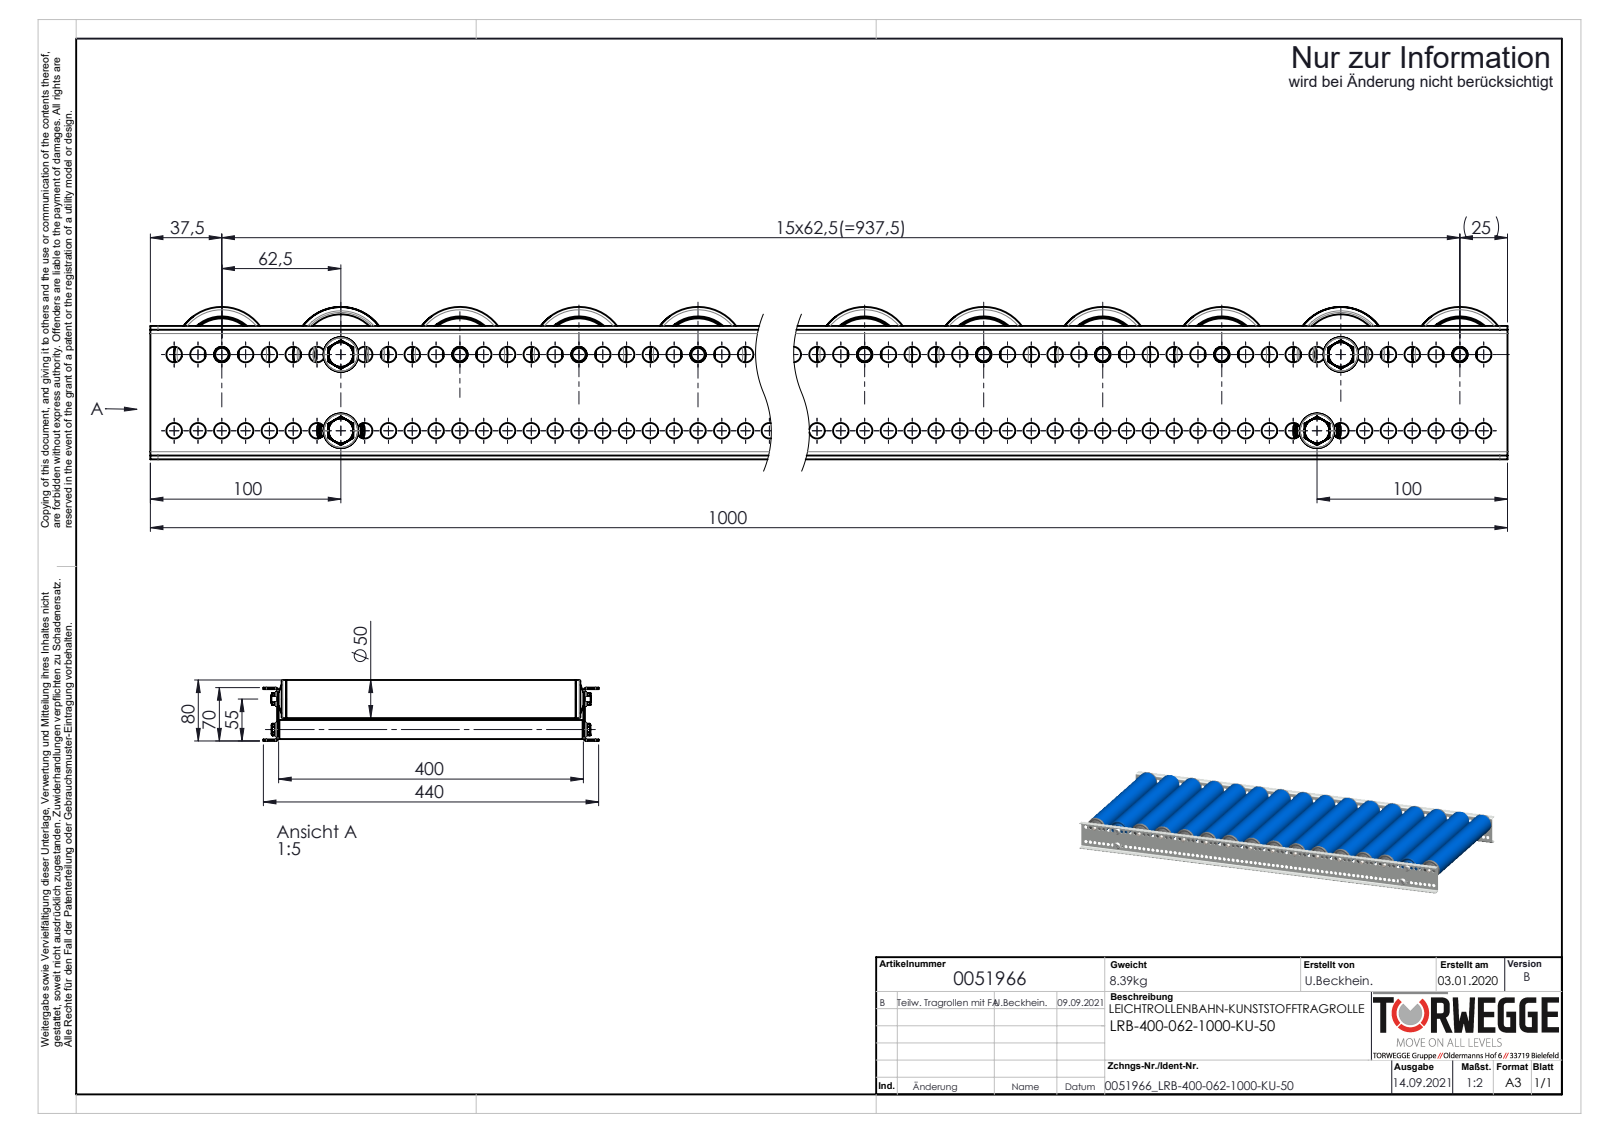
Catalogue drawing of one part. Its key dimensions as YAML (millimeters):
part_name: "Sicherungsring_DIN471_8x0.8_Circlip DIN 471 - 8 x 0.8; 0026267_Typ-KUT100-50x2,8-8_Lageboden-schematisch; S100994_Sperrzahnschraube_M08x16-8.8-A2K; 0017015_Tragrollenrohr-Ø50x2,8KU_KFG_0017015_L=380 (+8 more)"
step_written_by: "SolidWorks 2020 (AUTOMOTIVE_DESIGN)"
units: millimeters
bodies: {solids: 274, faces: 5068, planar: 1336, cylindrical: 2192, other: 1540}
overall_size: [1000, 440, 80]
volume: 4299000
surface_area: 3194000
round_holes:
  - {diameter: 8.2, count: 158}
  - {diameter: 7.6, count: 14}
  - {diameter: 8, count: 14}
  - {diameter: 25, count: 14}
  - {diameter: 30, count: 14}
  - {diameter: 35, count: 14}
  - {diameter: 39.4, count: 14}
  - {diameter: 40, count: 14}
  - {diameter: 6.8, count: 4}
  - {diameter: 12, count: 2}
  - {diameter: 12.1, count: 2}
  - {diameter: 16, count: 2}
round_bosses_or_shafts:
  - {diameter: 50, count: 16}
  - {diameter: 44.4, count: 14}
  - {diameter: 38, count: 14}
  - {diameter: 36, count: 14}
  - {diameter: 33, count: 14}
  - {diameter: 22, count: 14}
  - {diameter: 21, count: 14}
  - {diameter: 25, count: 4}
partial_cylinders:
  - {radius: 0.6, count: 28}
  - {radius: 0.75, count: 28}
  - {radius: 2.45, count: 28}
  - {radius: 4.87, count: 14}
  - {radius: 7, count: 14}
  - {radius: 4, count: 8}
  - {radius: 2, count: 4}
  - {radius: 2.5, count: 4}
face_to_face_distances: [2, 402, 68, 400, 404, 392, 66, 70, 12, 6]
hole_center_spacings: [12.5, 25, 37.5, 50, 62.5, 75, 87.5, 100]
